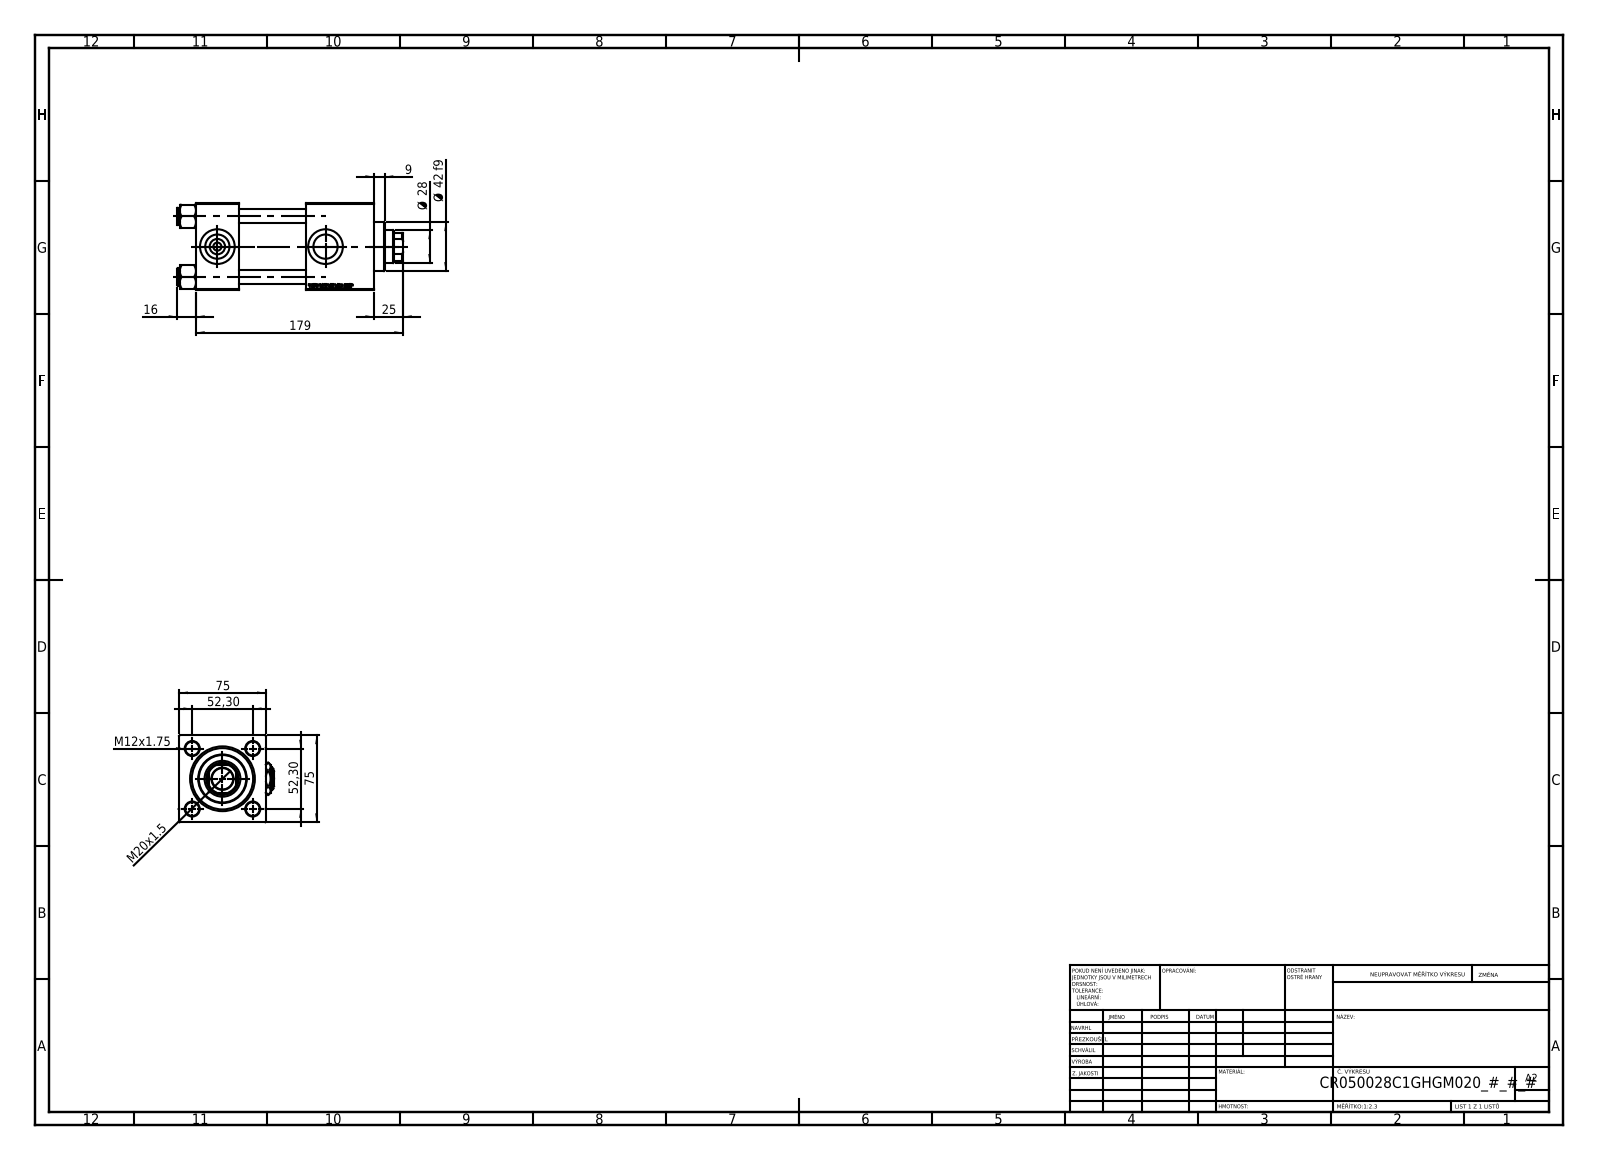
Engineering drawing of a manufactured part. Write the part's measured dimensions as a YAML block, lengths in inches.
part_name: "Zatka_pro_OIL_PORT; V215CR_VCP_C; V215CR_C_TYCINKA; V215CR_C_Body (+2 more)"
step_written_by: "SolidWorks 2019 (CONFIG_CONTROL_DESIGN)"
units: inches
bodies: {solids: 12, faces: 1195, planar: 549, cylindrical: 90, other: 556}
overall_size: [7.677, 3.239, 2.953]
volume: 40.62
surface_area: 237
round_holes:
  - {diameter: 0.472, count: 4}
  - {diameter: 0.276, count: 2}
  - {diameter: 0.825, count: 2}
  - {diameter: 1.181, count: 2}
  - {diameter: 0.728, count: 1}
  - {diameter: 1.102, count: 1}
  - {diameter: 1.22, count: 1}
  - {diameter: 1.614, count: 1}
  - {diameter: 1.969, count: 1}
  - {diameter: 2.087, count: 1}
round_bosses_or_shafts:
  - {diameter: 0.591, count: 4}
  - {diameter: 2.205, count: 1}
  - {diameter: 1.654, count: 1}
partial_cylinders:
  - {radius: 0.531, count: 1}
face_to_face_distances: [2.953, 1.457, 6.063, 4.606, 3.74, 2.323, 2.283, 4.933, 3.476, 1.193]
hole_center_spacings: [1.456, 2.059, 2.912, 3.681]
